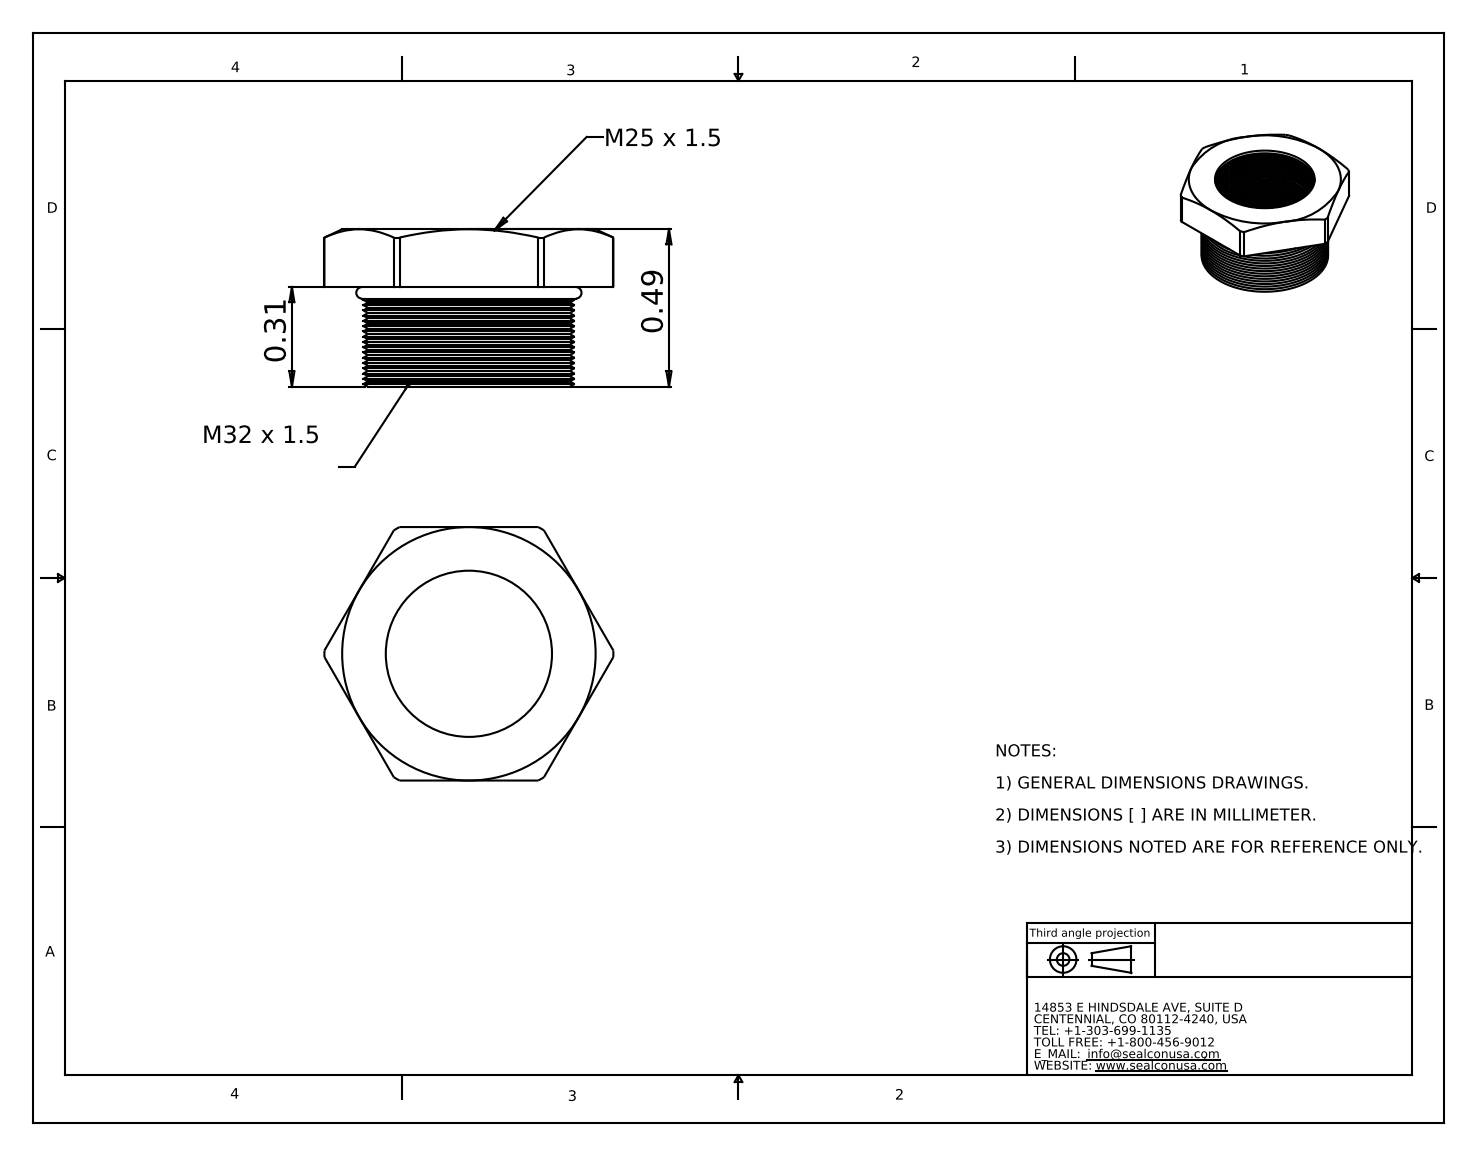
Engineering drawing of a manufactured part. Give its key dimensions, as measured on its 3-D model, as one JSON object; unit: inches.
{"part_name": "RM-3225-SS-B", "step_written_by": "SolidWorks 2008 (CONFIG_CONTROL_DESIGN)", "units": "inches", "bodies": {"solids": 2, "faces": 313, "planar": 9, "cylindrical": 105, "other": 199}, "overall_size": [0.901, 0.79, 0.49], "volume_in3": 0.094, "surface_area_in2": 4.155, "round_holes": [[0.518, 1]], "round_bosses_or_shafts": [[0.63, 1]], "partial_cylinders_radius": [[0.45, 1]], "face_to_face_distances": [0.18, 0.79, 0.31, 0.49]}
